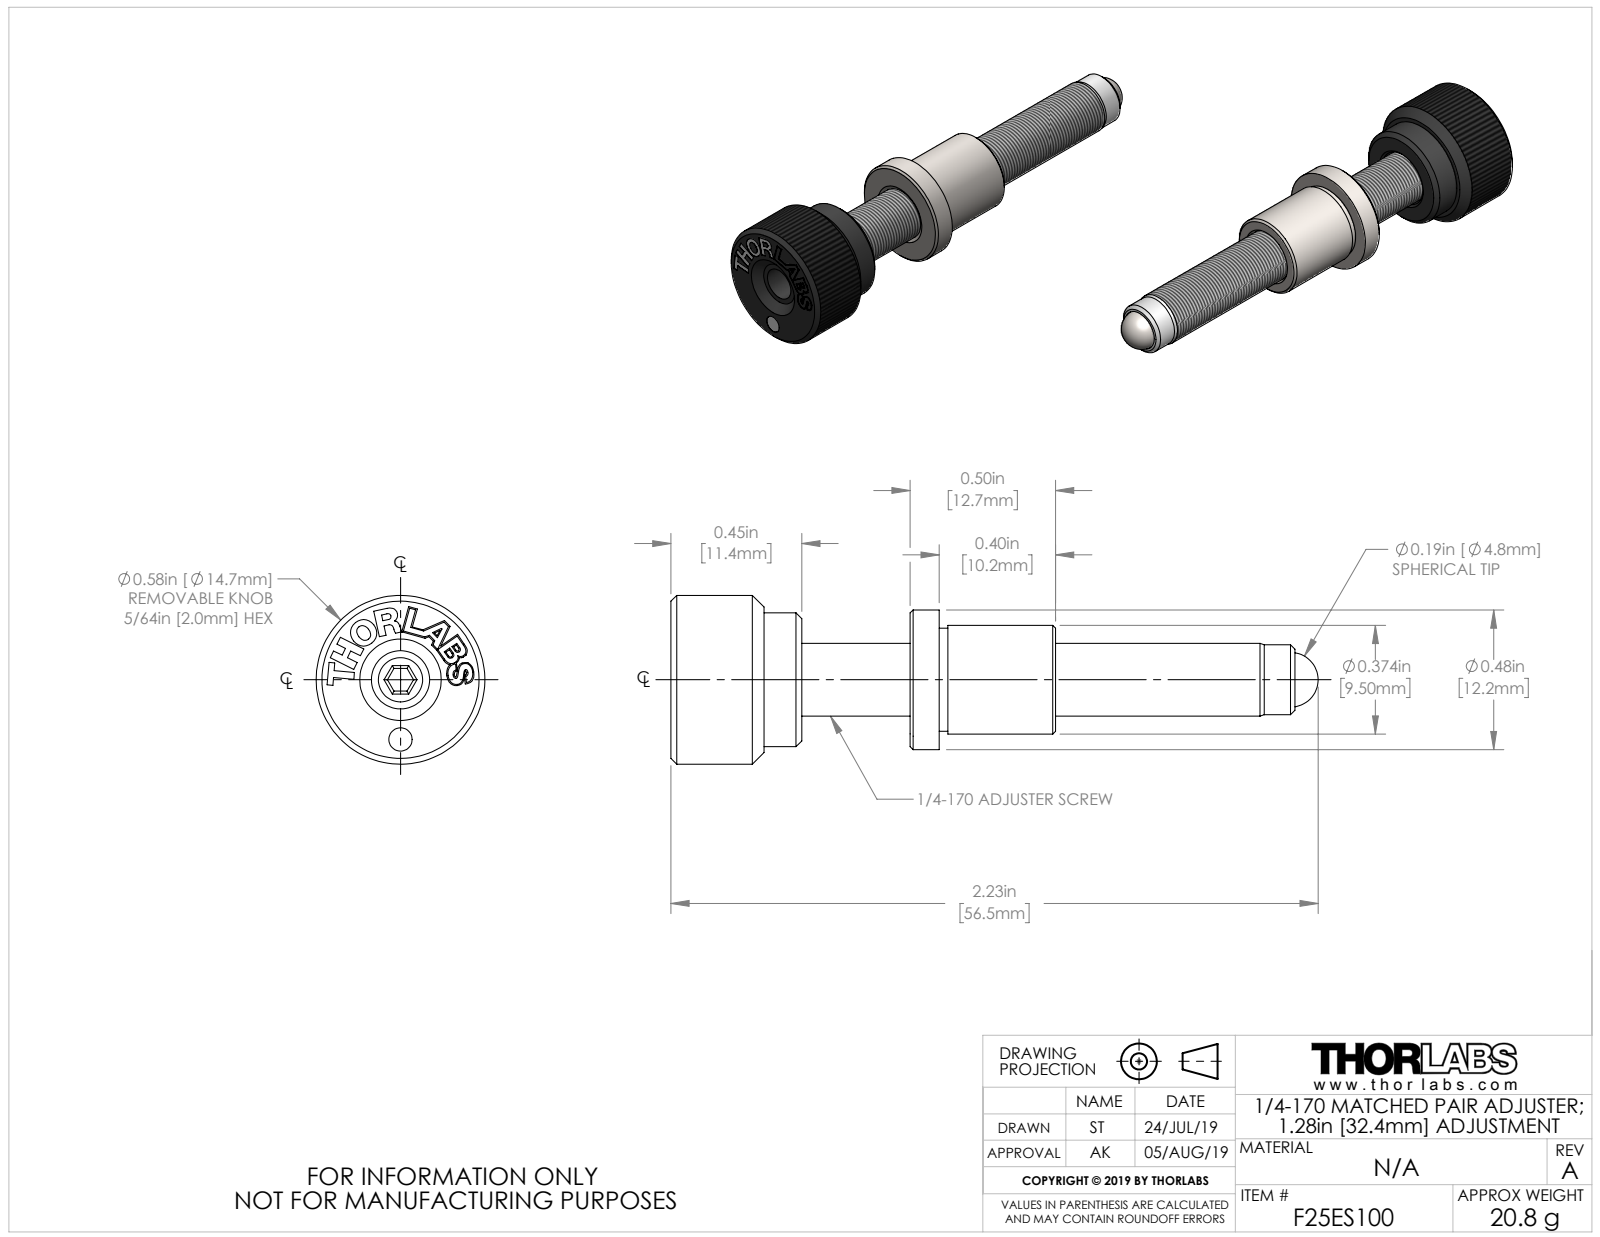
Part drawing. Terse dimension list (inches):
name: TTN192477-E0W
written by: SolidWorks 2018 (AUTOMOTIVE_DESIGN)
unit: in
bodies: 4 solids, 265 faces (139 planar, 37 cylindrical, 89 other)
size: 2.225 × 0.58 × 0.58
volume: 0.217 in³; area: 4.511 in²
holes: 1× ⌀0.08, 1× ⌀0.152, 1× ⌀0.188, 1× ⌀0.245, 1× ⌀0.265, 1× ⌀0.29
bosses: 1× ⌀0.58, 1× ⌀0.48, 1× ⌀0.46, 1× ⌀0.374, 1× ⌀0.354, 1× ⌀0.25, 1× ⌀0.24, 1× ⌀0.21
rounds: 1× R0.014, 1× R0.047, 1× R0.059
face distances: 0.822, 0.1, 0.552, 0.922, 0.27, 0.652, 0.45, 0.18, 0.372, 0.472
hole spacings: 0.205
